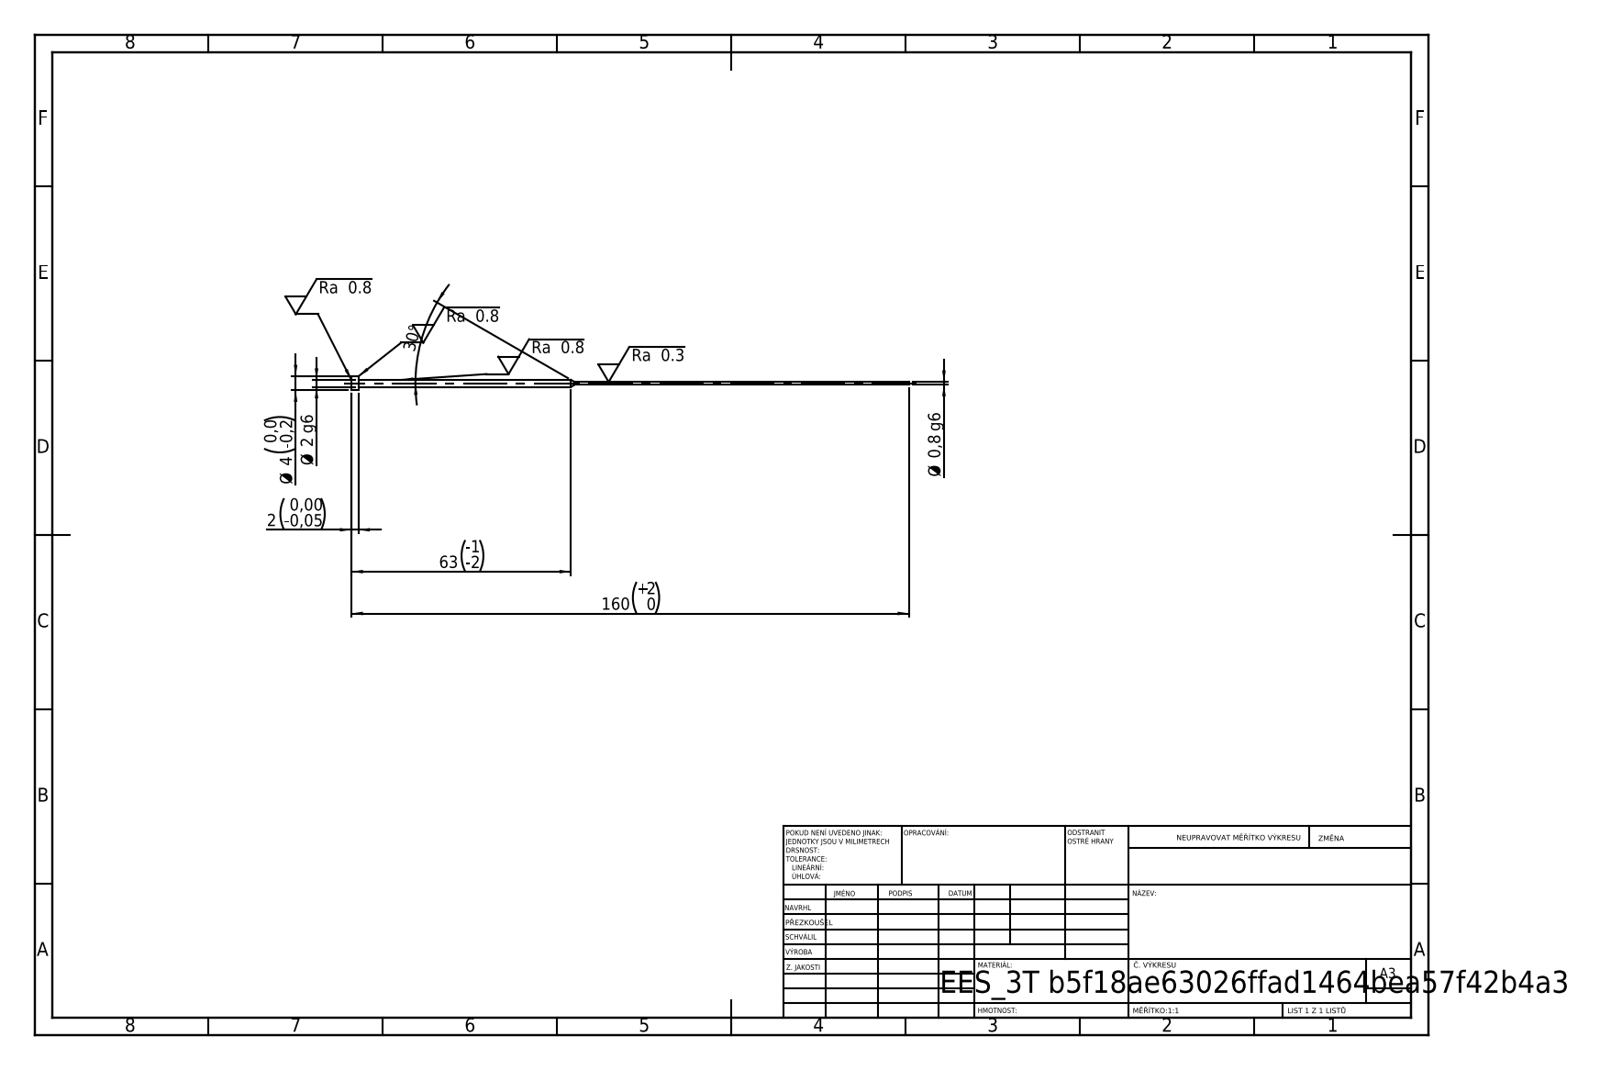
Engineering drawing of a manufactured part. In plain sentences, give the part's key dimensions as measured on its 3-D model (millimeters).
Its 3-D file was written by "SolidWorks 2019 (CONFIG_CONTROL_DESIGN)". It is 1 solid with 11 faces: 3 planar, 6 cylindrical and 2 other. Overall it measures 160 by 4 by 4 millimeters. Its volume is 267 cubic millimeters and its surface area 677 square millimeters. Round bosses or shafts: 1 of diameter 4, 1 of diameter 2, 1 of diameter 0.8. The main face-to-face distances are 2, 158, 160.
